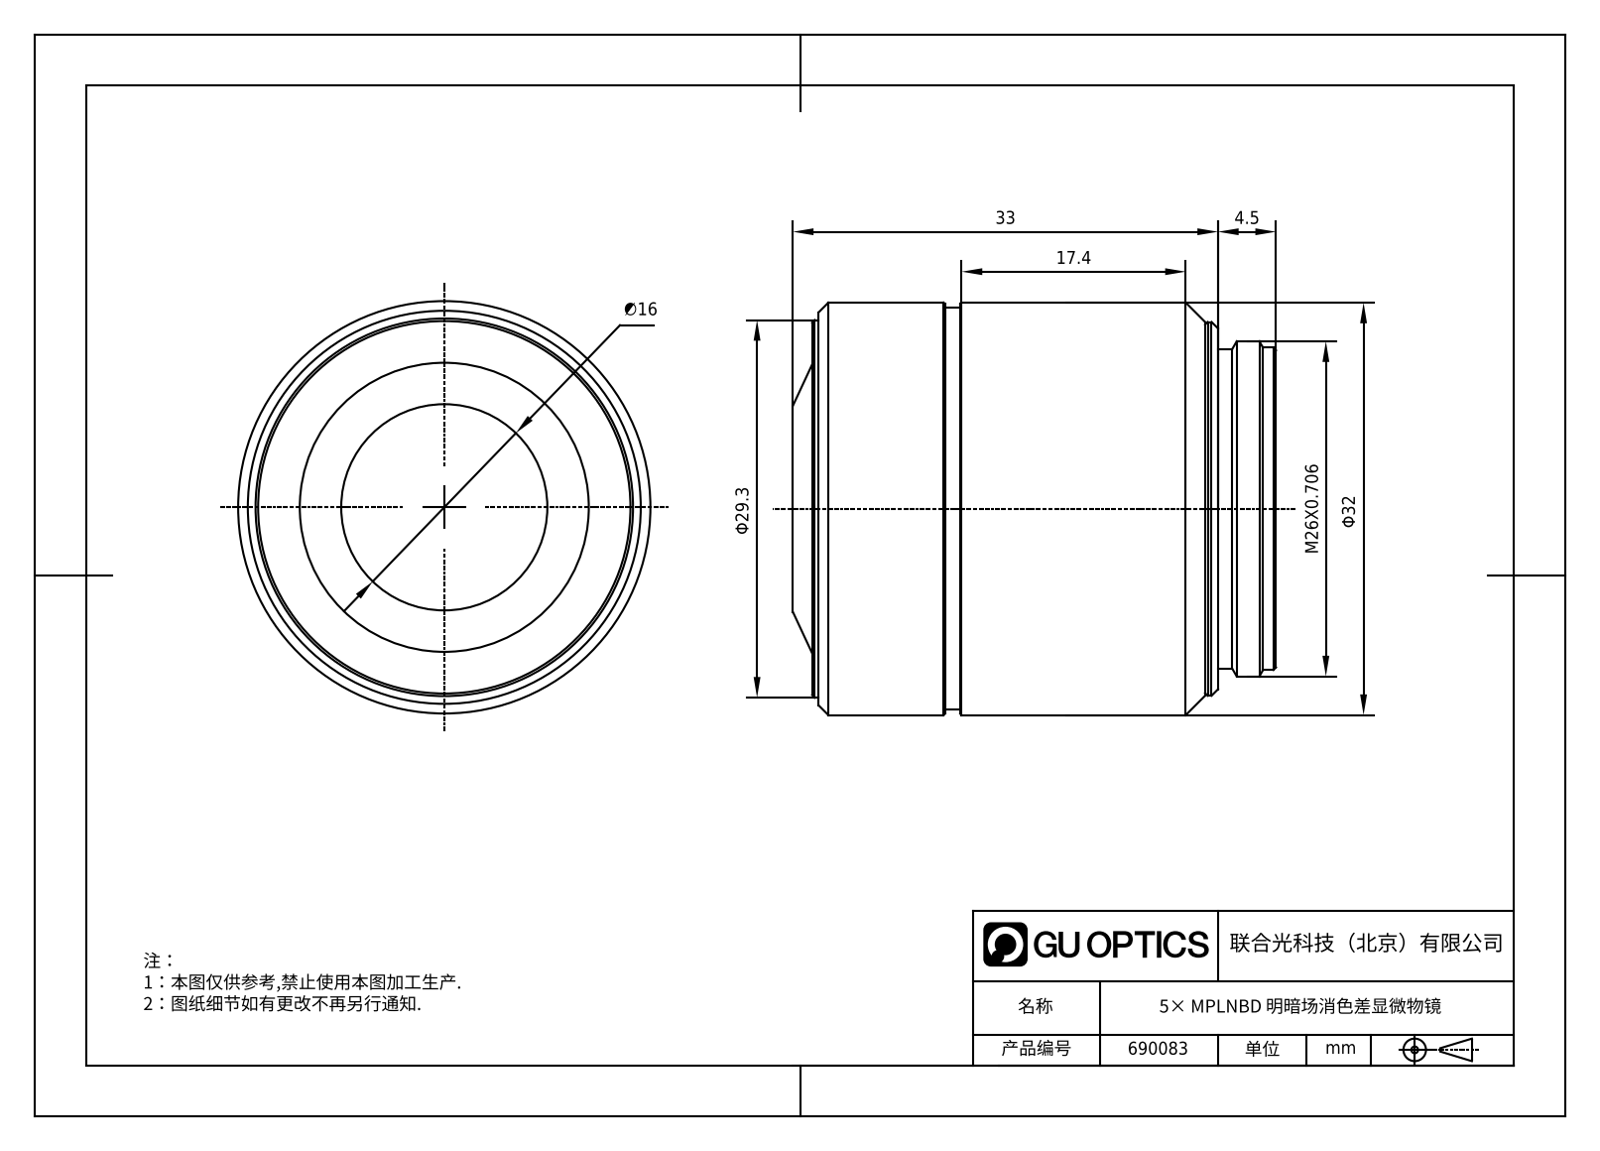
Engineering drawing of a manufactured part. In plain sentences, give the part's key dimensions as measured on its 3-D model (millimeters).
The part is named "690083". Its 3-D file was written by "SolidWorks 2020 (CONFIG_CONTROL_DESIGN)". It is 1 solid with 46 faces: 8 planar, 16 cylindrical and 22 other. Overall it measures 37.5 by 32 by 32 millimeters. Its volume is 27 643 cubic millimeters and its surface area 5 107 square millimeters. Round bosses or shafts: 1 of diameter 32, 1 of diameter 31.2, 1 of diameter 29.3, 1 of diameter 29, 1 of diameter 26, 1 of diameter 25, 1 of diameter 24.78. The main face-to-face distances are 36, 1.5, 37.5, 33, 31.5, 4.5, 2, 0.5, 31, 35.5.
